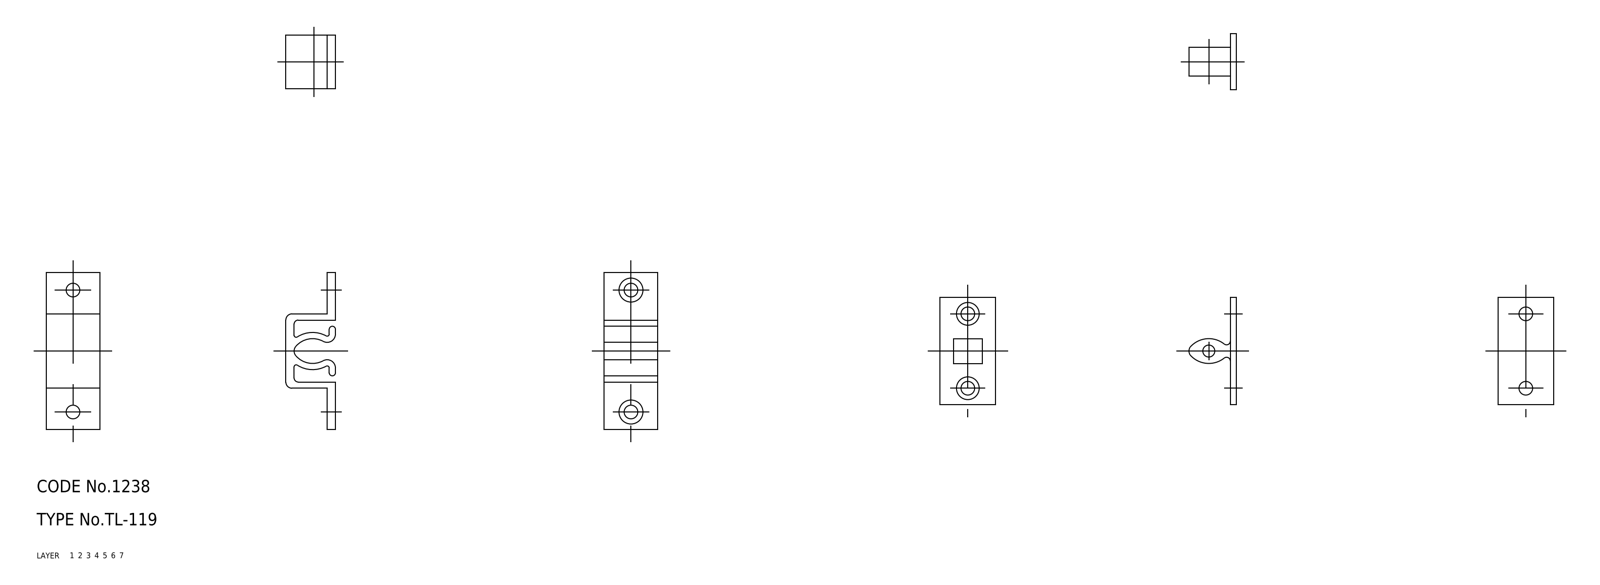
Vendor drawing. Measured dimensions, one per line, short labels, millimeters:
name: keeper; base; TL_119_10679_36
written by: CADfix (AUTOMOTIVE_DESIGN)
unit: mm
bodies: 2 solids, 67 faces (0 planar, 0 cylindrical, 67 other)
size: 45.97 × 38 × 13.5
volume: 2 568 mm³; area: 3 497 mm²
